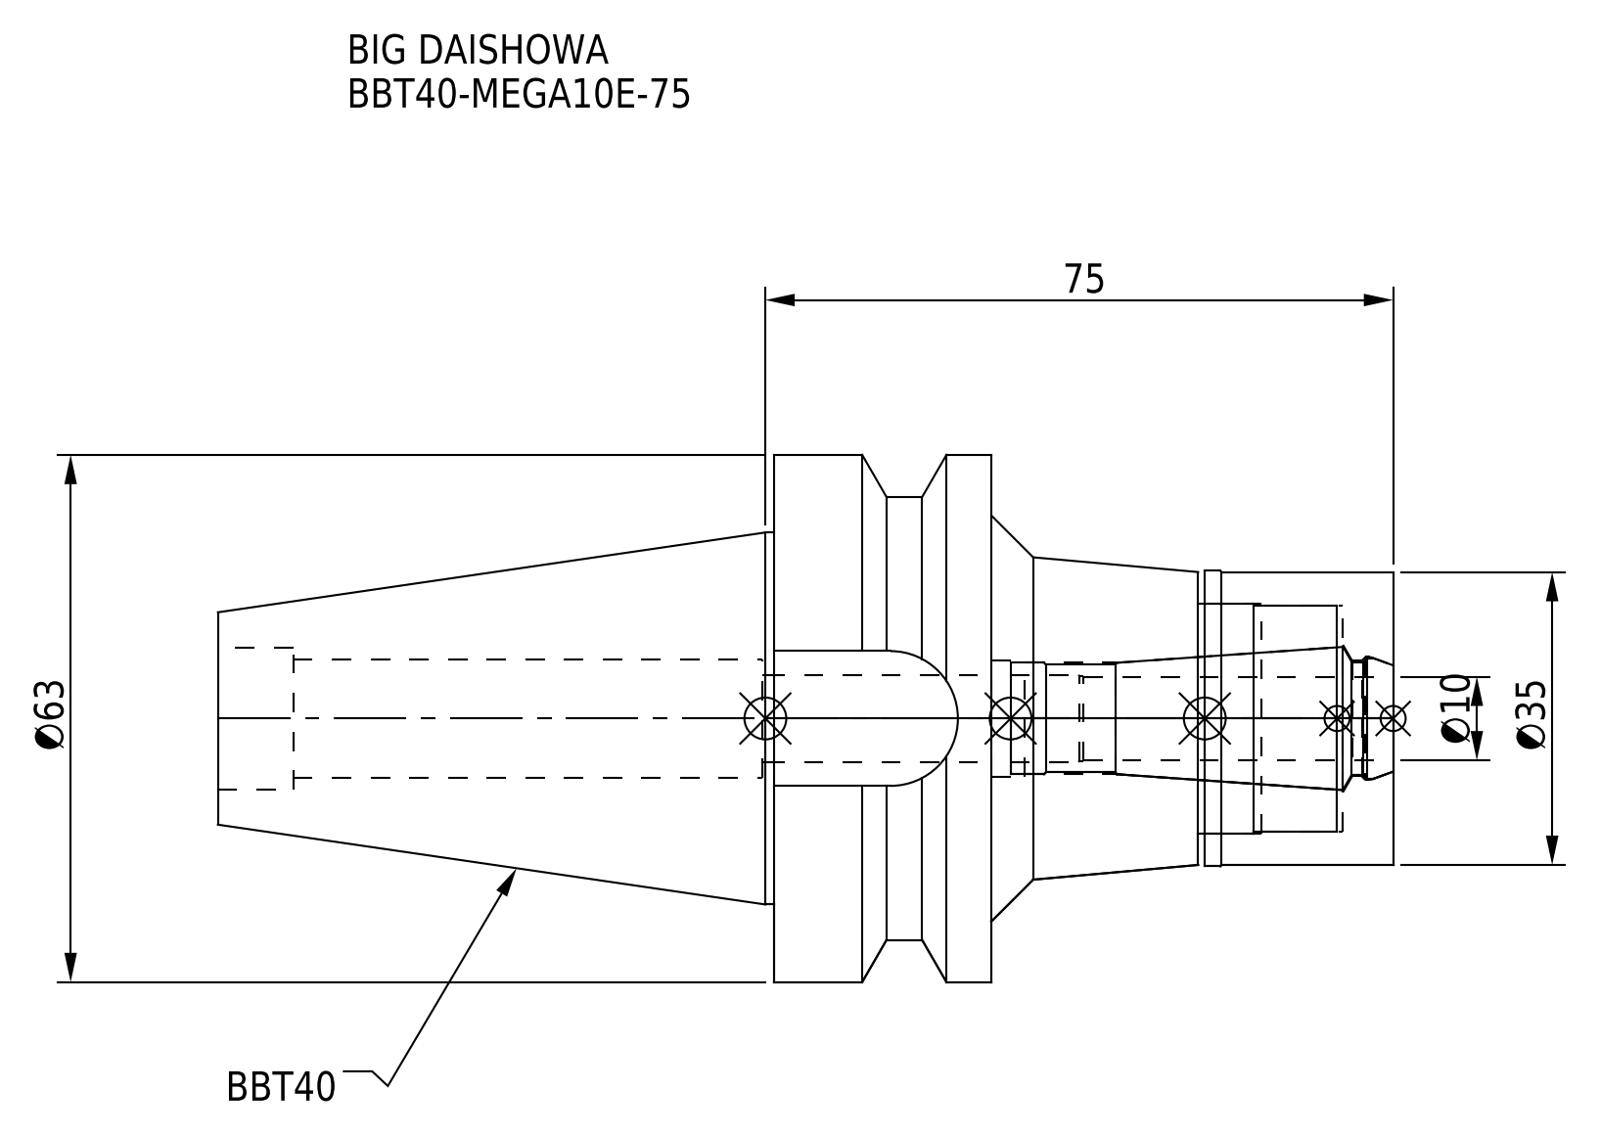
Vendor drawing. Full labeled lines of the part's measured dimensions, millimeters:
Part name (STEP PRODUCT): MEN10_1.stp; BBT40-MEGA10E-75_1.stp; BBT40-MEGA10E-75; DXF_TEMP_ASSY_ASM_4_ASM.stp (+3 more)
STEP written by: SolidWorks 2019 (CONFIG_CONTROL_DESIGN)
Units: millimetres
Bodies: 2 solids, 78 faces (20 planar, 38 cylindrical, 20 other)
Overall size (bounding box): 140.4 × 63 × 63
Volume: 164 600 mm³ · Surface area: 33 928 mm²
Round holes (diameter × count): ⌀10.4 ×1, ⌀13.3 ×1, ⌀13.8 ×1, ⌀13.9 ×1, ⌀14.2 ×1, ⌀14.7 ×1, ⌀17 ×1, ⌀27 ×1, ⌀27.5 ×1
Round bosses / shafts (diameter × count): ⌀63 ×1, ⌀53 ×1, ⌀44.45 ×1, ⌀35.3 ×1, ⌀35 ×1
Partial cylindrical surfaces — rounded edges, fillets, slot ends (radius × count): R8.05 ×1
Main face-to-face distances: 26, 48, 74, 22.5, 25.5, 51.5, 23.3, 0.8, 24.7, 50.7
